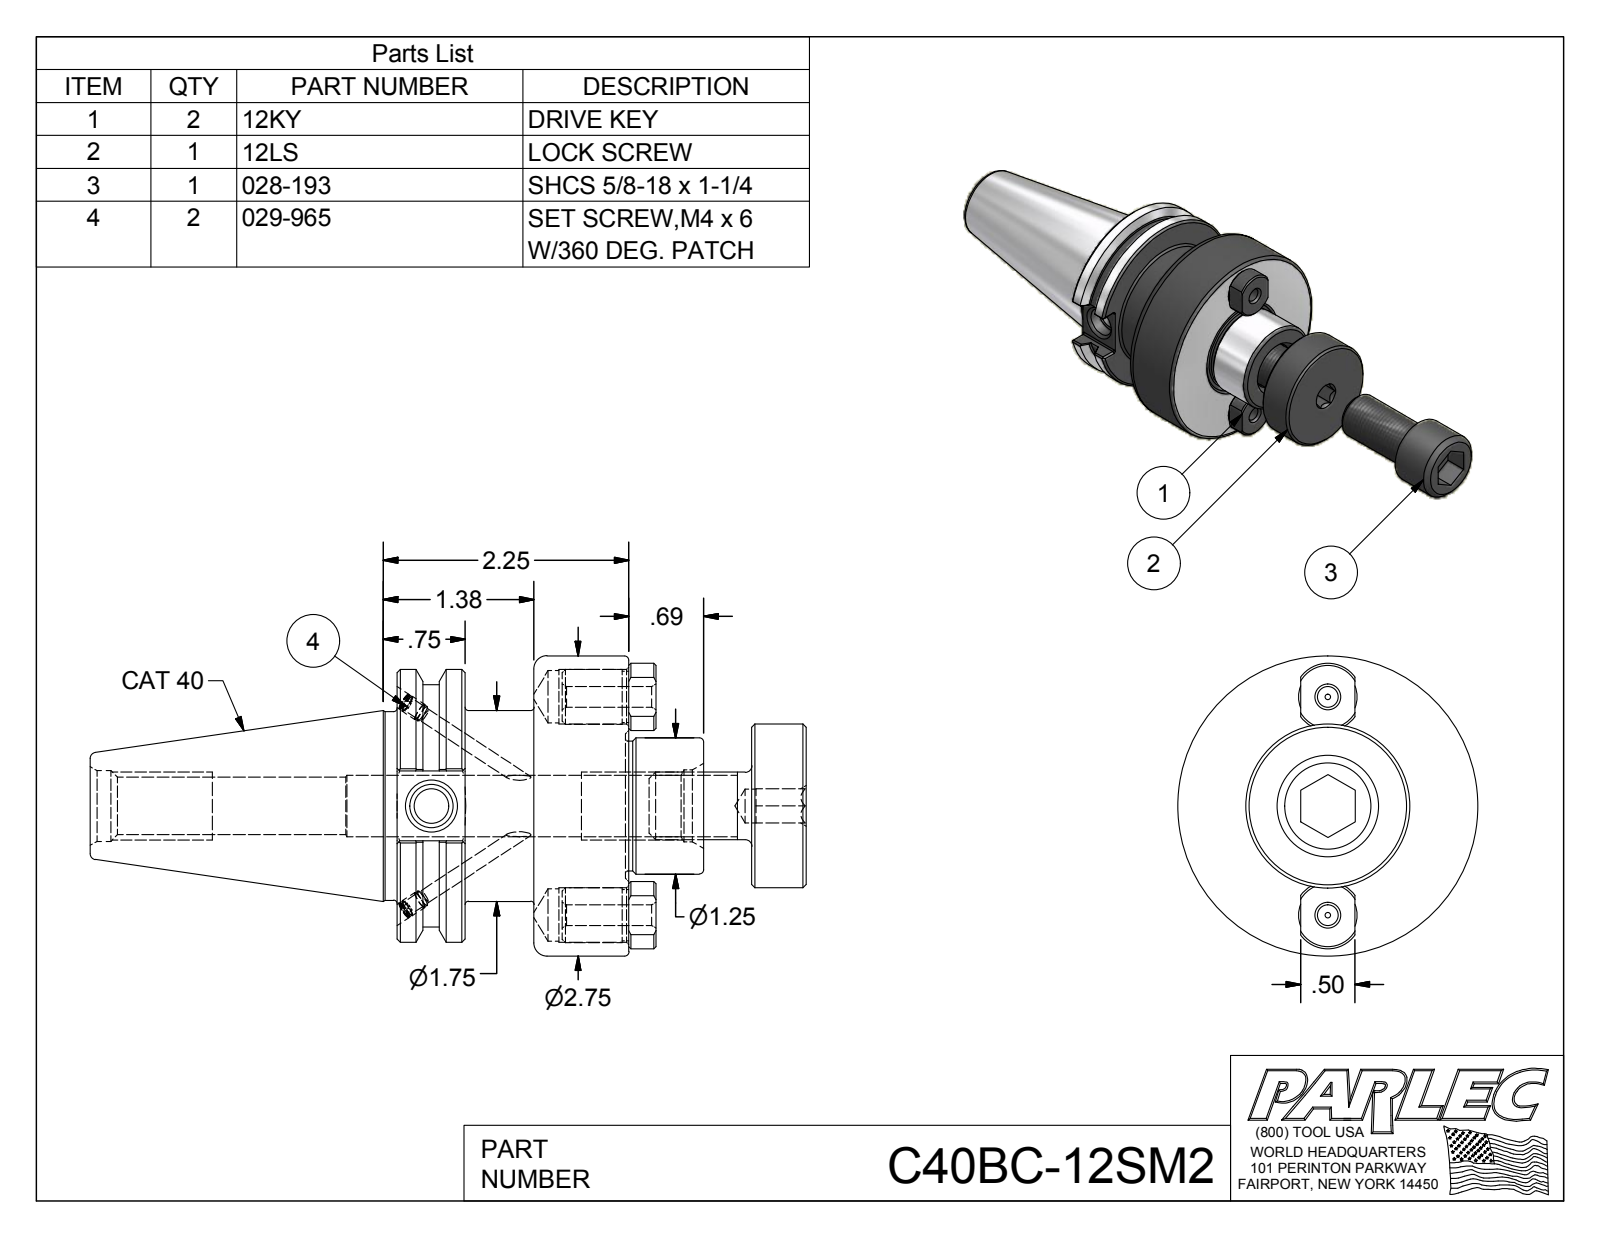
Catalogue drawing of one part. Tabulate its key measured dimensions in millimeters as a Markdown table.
| quantity | value |
| --- | --- |
| part name | C40BC-12SM2; C40BC-12SM2-1; 12KY; 028-193 (+2 more) |
| STEP written by | Autodesk Inventor 2012 (AUTOMOTIVE_DESIGN) |
| units | millimeters |
| bodies | 7 solids, 215 faces (90 planar, 58 cylindrical, 67 other) |
| overall size | 228.4 × 69.9 × 69.9 |
| volume | 242 900 mm³ |
| surface area | 50 280 mm² |
| round holes (diameter × count) | 3.3 × 2, 4.1 × 2, 4.8 × 2, 12.2 × 2, 12.7 × 2, 7.9 × 1, 8 × 1, 10.1 × 1, 13.4 × 1, 14.4 × 1, 16.5 × 1, 16.8 × 1 |
| round bosses / shafts (diameter × count) | 12.8 × 2, 11.9 × 2, 4.2 × 2, 4 × 2, 69.9 × 1, 63.5 × 1, 56.4 × 1, 44.5 × 1 |
| partial cylindrical surfaces (radius × count) | 0.5 × 12, 7.8 × 2 |
| main face-to-face distances | 22.1, 38.1, 31.9, 54, 15.9, 16, 12.7, 95.3, 79.4, 63.4 |
| hole center spacings | 25.4, 50.8 |
